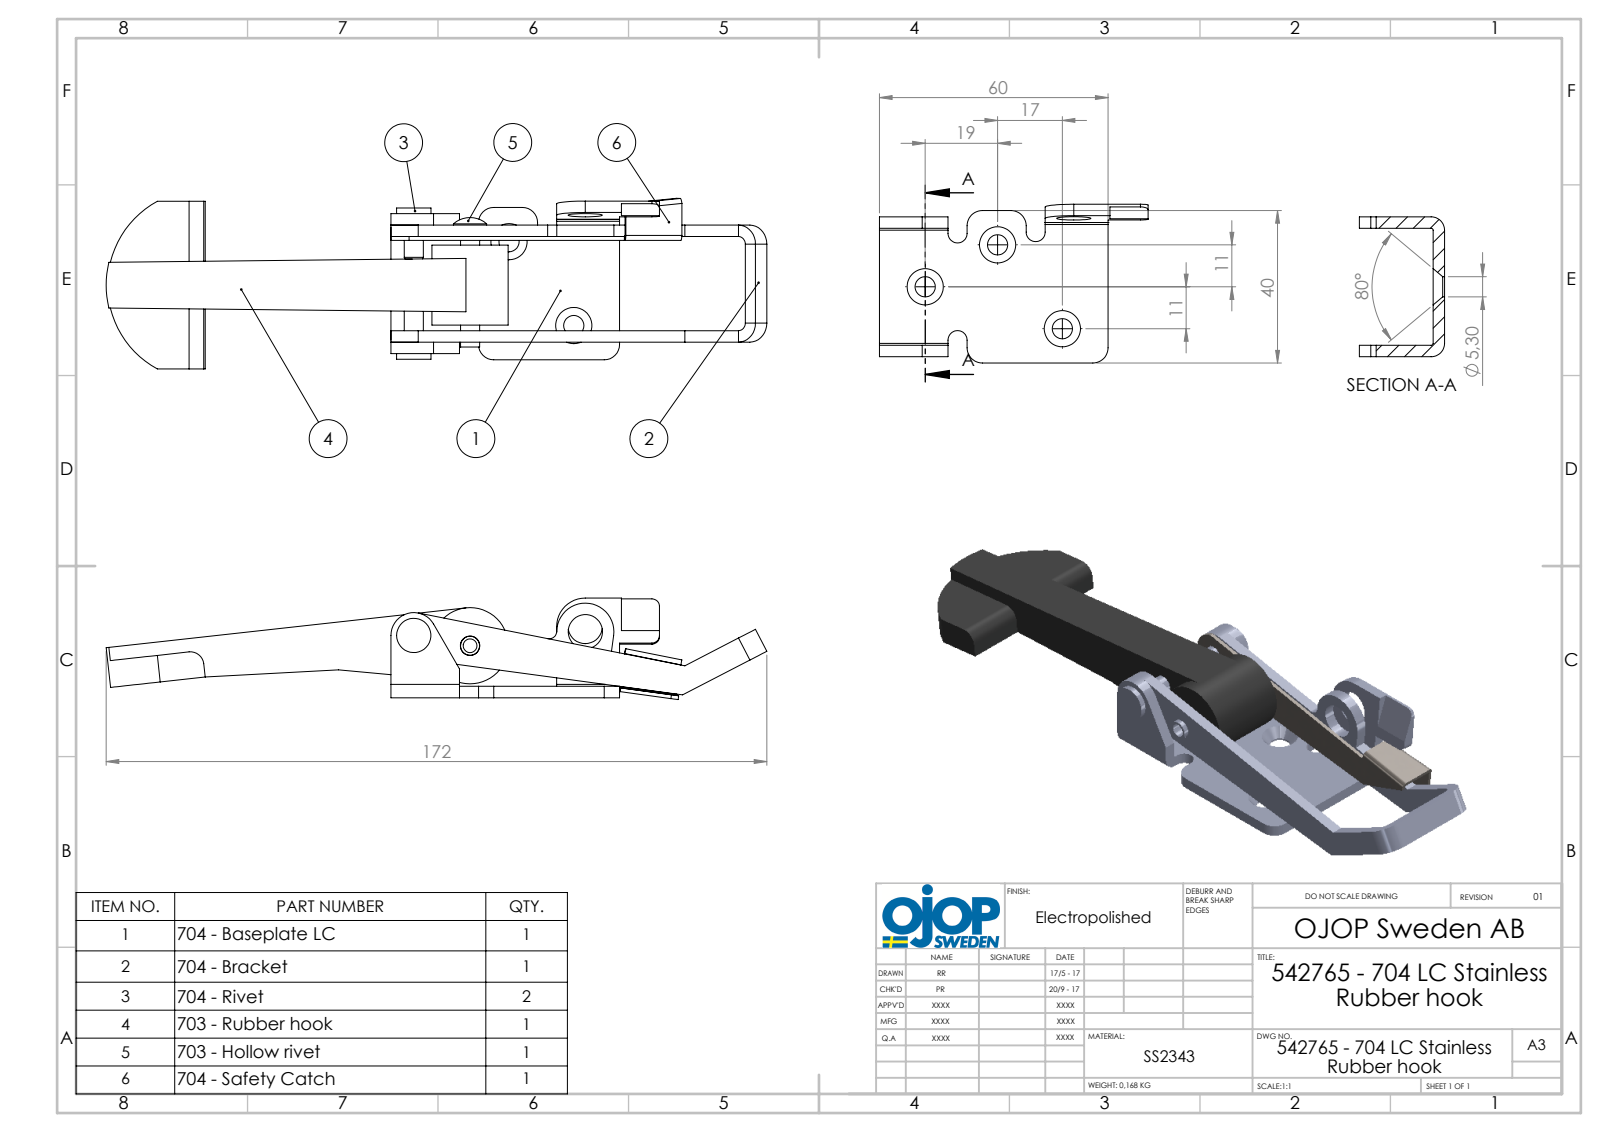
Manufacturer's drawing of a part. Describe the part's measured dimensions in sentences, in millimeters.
The part is named "74286 - Platta 704 LC RF Spärr; 74123 - Bygel 704 RF Låsögla; 704 - Rivet Gradin; gummihake 703 (+3 more)". Its 3-D file was written by "SolidWorks 2015 (AUTOMOTIVE_DESIGN)". It is 7 solids with 219 faces: 115 planar, 90 cylindrical and 14 other. Overall it measures 173.43 by 44.79 by 26.4 millimeters. Its volume is 41 270 cubic millimeters and its surface area 24 920 square millimeters. Round holes: 3 of diameter 5.3, 2 of diameter 5.1, 2 of diameter 9, 1 of diameter 2.5, 1 of diameter 5.4, 1 of diameter 5.5, 1 of diameter 7.2. Round bosses or shafts: 2 of diameter 5, 1 of diameter 20, 1 of diameter 9, 1 of diameter 7. Partial cylindrical surfaces (rounded edges, fillets, slot ends): 5 of radius 2, 4 of radius 3.5, 4 of radius 4, 3 of radius 0.3, 3 of radius 0.5, 3 of radius 1.3, 3 of radius 2.5, 2 of radius 5. The main face-to-face distances are 3, 27.7, 30.7, 10.5, 1, 24.7, 4, 23.7, 26.7, 3.49. The hole center spacings are 15.02, 21.95, 27.8, 30.5, 37.64, 45.05.
